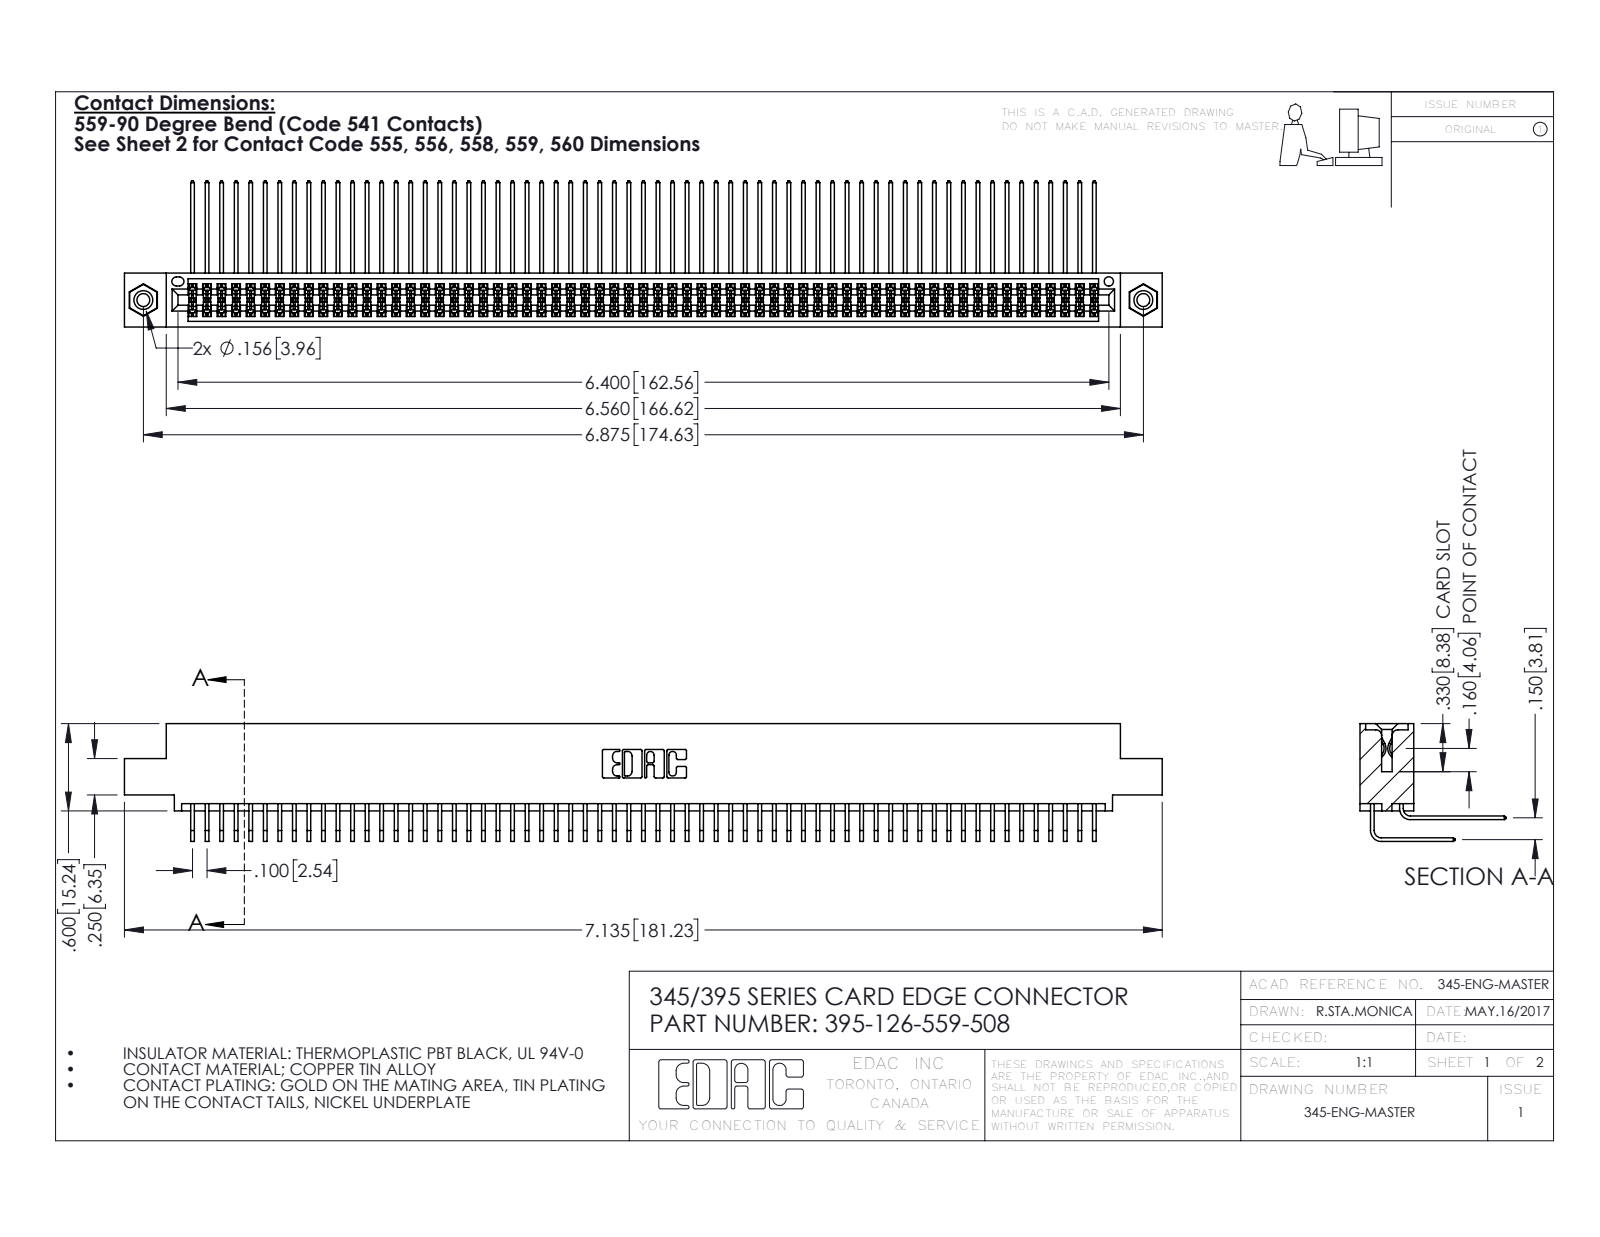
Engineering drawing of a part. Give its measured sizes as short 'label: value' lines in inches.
name: 345-292-001_558 559 Tail - 1; 345-292-001_559 Tail - 2; 345-250-001_345-250-003-102; 345 Part_0.110 Offset - 0.156 Dia-TI (+1 more)
written by: SolidWorks 2016 (CONFIG_CONTROL_DESIGN)
unit: in
bodies: 129 solids, 6742 faces (4526 planar, 2200 cylindrical, 16 other)
size: 7.135 × 1.005 × 0.809
volume: 1.126 in³; area: 48.36 in²
holes: 2× ⌀0.089, 2× ⌀0.125, 2× ⌀0.156, 1× ⌀0.064
bosses: 2× ⌀0.155
rounds: 190× R0.006, 22× R0.01, 6× R0.007, 6× R0.031, 3× R0.026, 2× R0.014, 2× R0.019, 2× R0.022
face distances: 0.072, 0.298, 0.2, 0.37, 0.098, 0.272, 0.025, 0.225, 0.175, 0.15
hole spacings: 0.27, 6.639, 6.875
